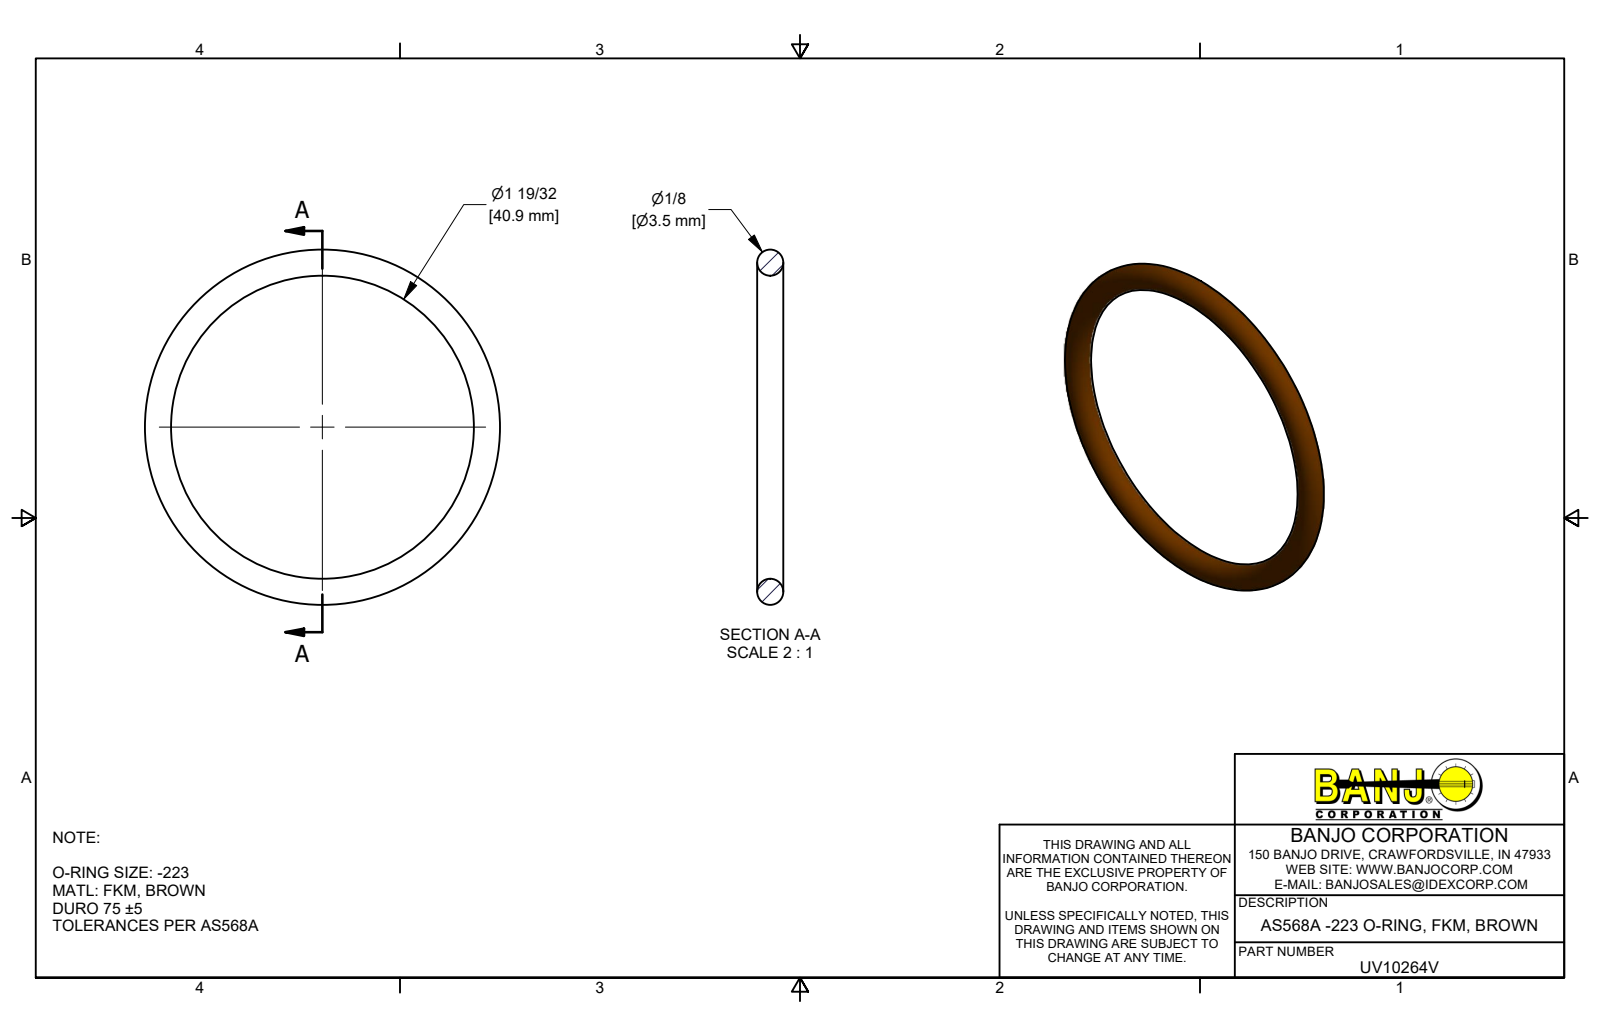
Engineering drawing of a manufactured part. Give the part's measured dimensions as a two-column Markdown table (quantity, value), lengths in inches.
| quantity | value |
| --- | --- |
| part name | UV10264V |
| STEP written by | Autodesk Inventor 2019 (AUTOMOTIVE_DESIGN) |
| units | inches |
| bodies | 1 solid, 1 faces (0 planar, 0 cylindrical, 1 other) |
| overall size | 1.887 × 1.887 × 0.139 |
| volume | 0.083 in³ |
| surface area | 2.398 in² |
